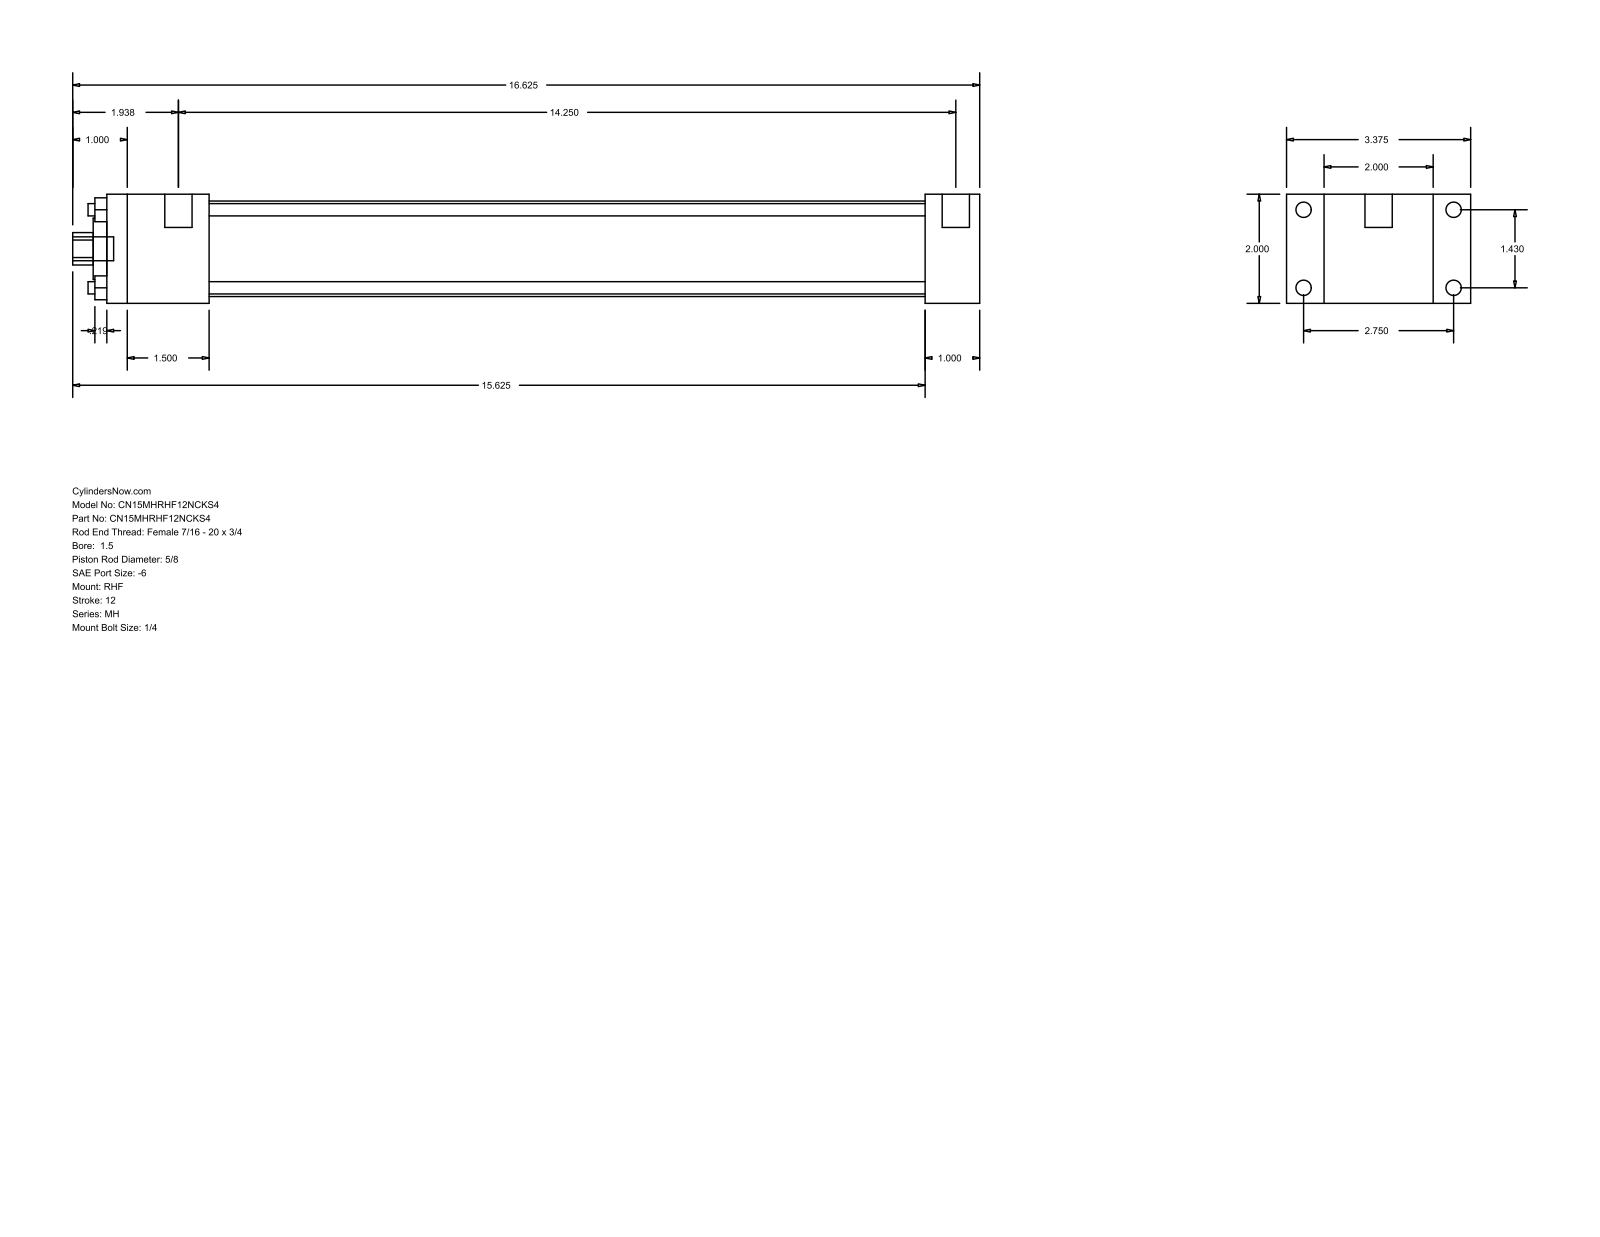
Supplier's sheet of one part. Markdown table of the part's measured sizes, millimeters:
| quantity | value |
| --- | --- |
| part name | MH_RHF__0150_0.625 |
| STEP written by | GSSL Pune (CONFIG_CONTROL_DESIGN) |
| units | millimeters |
| bodies | 0 solids, 88 faces (60 planar, 28 cylindrical, 0 other) |
| overall size | 422.27 × 85.72 × 50.8 |
| round holes (diameter × count) | 5.71 × 4, 15.88 × 1, 28.57 × 1, 44.45 × 1 |
| round bosses / shafts (diameter × count) | 7.14 × 4, 5.56 × 4, 12.7 × 2, 11.11 × 1 |
| partial cylindrical surfaces (radius × count) | 7.54 × 1 |
| main face-to-face distances | 50.8, 17.46, 68.26, 25.39, 381, 406.39, 85.72, 47.62, 333.38, 358.77 |
| hole center spacings | 25.68, 36.32, 51.36 |
